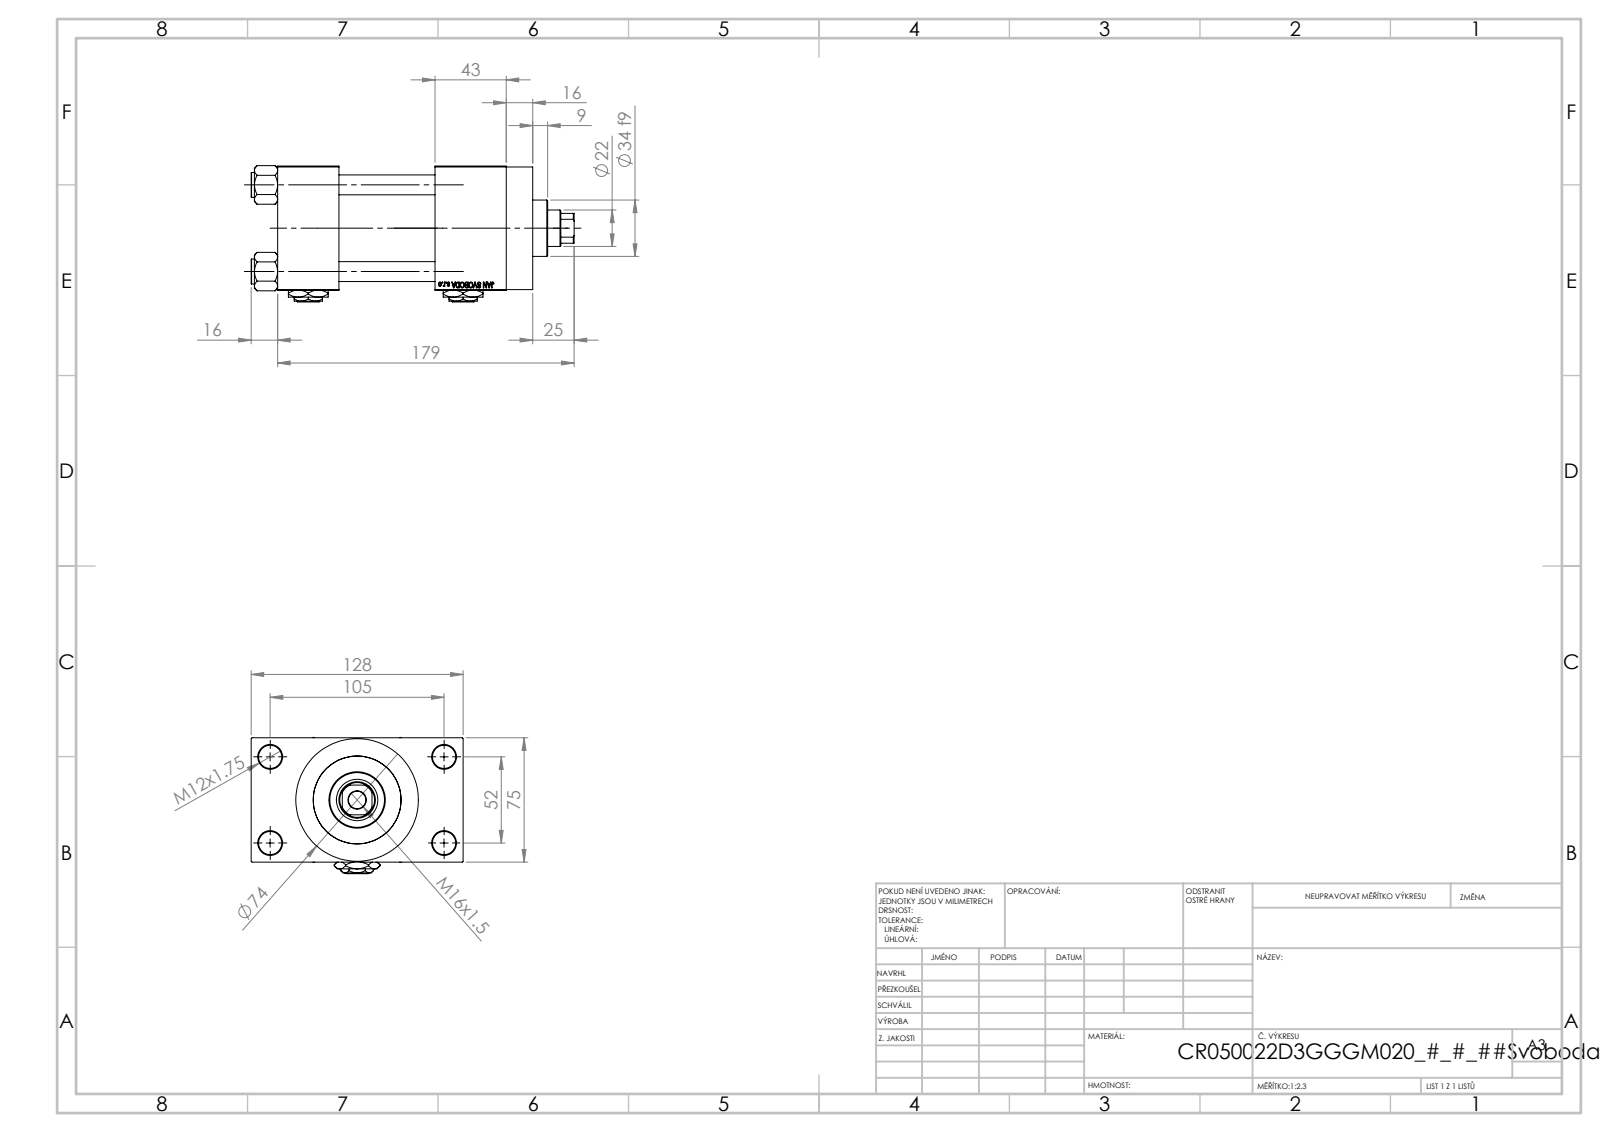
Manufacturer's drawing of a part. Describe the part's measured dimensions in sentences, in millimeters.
The part is named "Zatka_pro_OIL_PORT; V215CR_VCP_D; V215CR_D_TYCINKA; NUT_M5_D (+2 more)". Its 3-D file was written by "SolidWorks 2019 (CONFIG_CONTROL_DESIGN)". It is 13 solids with 1205 faces: 545 planar, 100 cylindrical and 560 other. Overall it measures 195 by 128 by 82.27 millimeters. Its volume is 802 177 cubic millimeters and its surface area 169 183 square millimeters. Round holes: 4 of diameter 12, 4 of diameter 14, 2 of diameter 7, 2 of diameter 20.96, 2 of diameter 30, 1 of diameter 10.5, 1 of diameter 22, 1 of diameter 25, 1 of diameter 41, 1 of diameter 50, 1 of diameter 53. Round bosses or shafts: 4 of diameter 15, 1 of diameter 74, 1 of diameter 56, 1 of diameter 34. Partial cylindrical surfaces (rounded edges, fillets, slot ends): 1 of radius 10.5. The main face-to-face distances are 75, 58, 37, 95, 26.5, 101.5, 138, 101, 43, 16. The hole center spacings are 26.35, 36.98, 52.3, 58.43, 58.59, 78.65, 94.37, 52.
